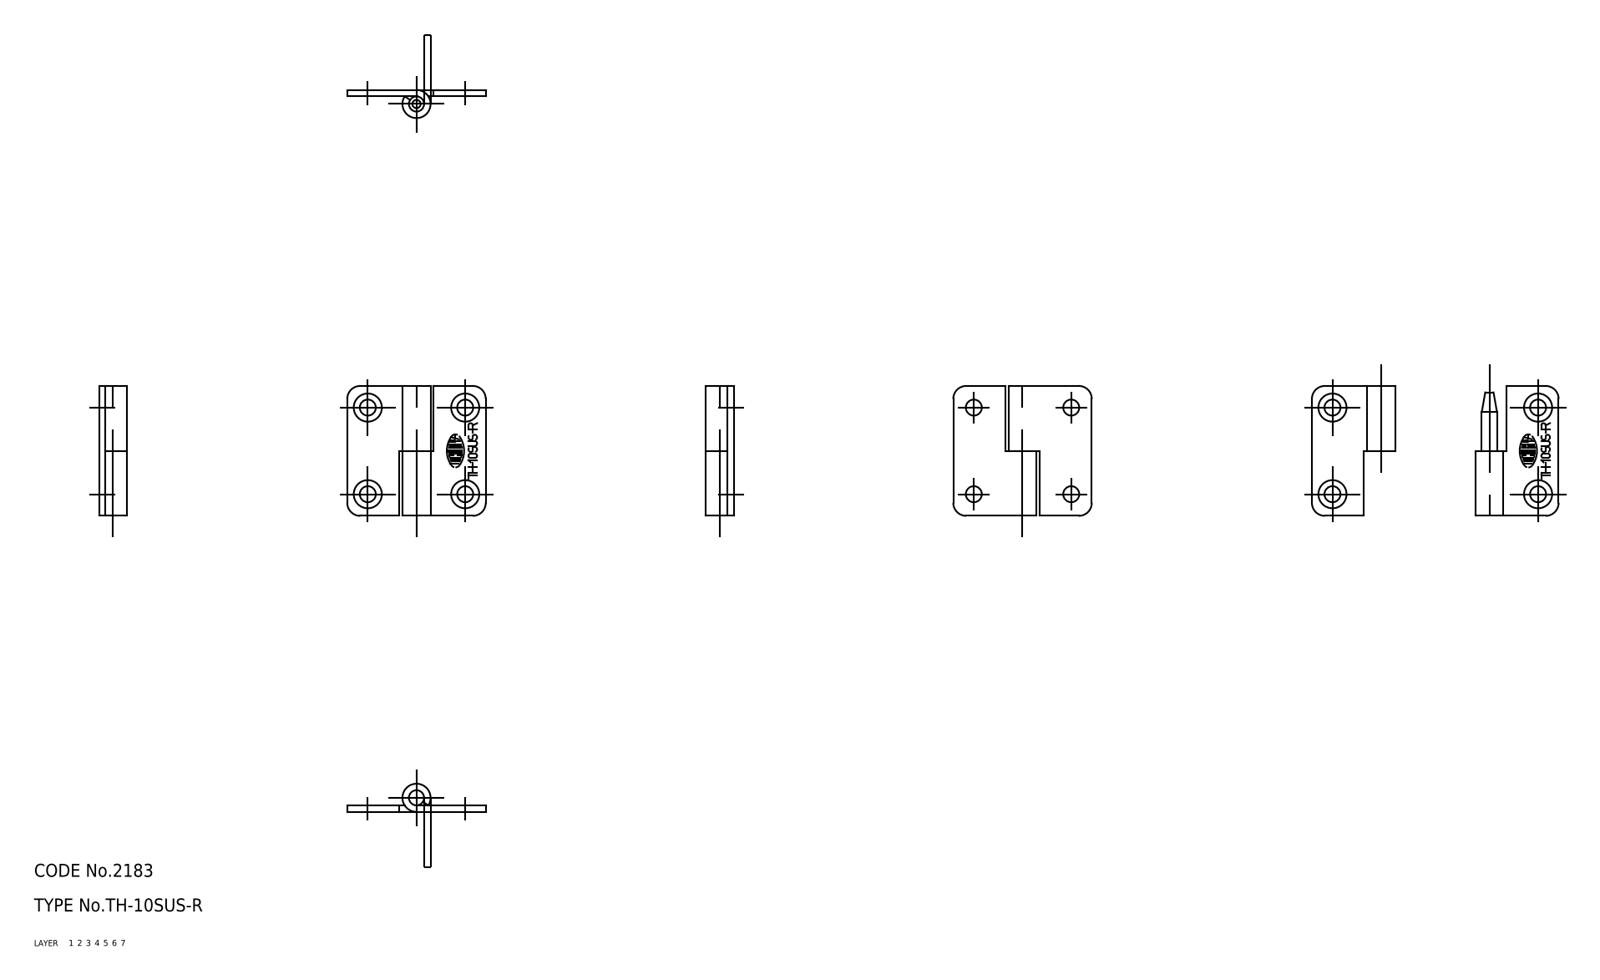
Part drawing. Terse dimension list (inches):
name: shaft; hinge piece_B; hinge piece_A; TH_10SUS_R_31987_36
written by: CADfix (AUTOMOTIVE_DESIGN)
unit: in
bodies: 3 solids, 46 faces (0 planar, 0 cylindrical, 46 other)
size: 1.26 × 1.181 × 0.256
volume: 0.121 in³; area: 4.762 in²
